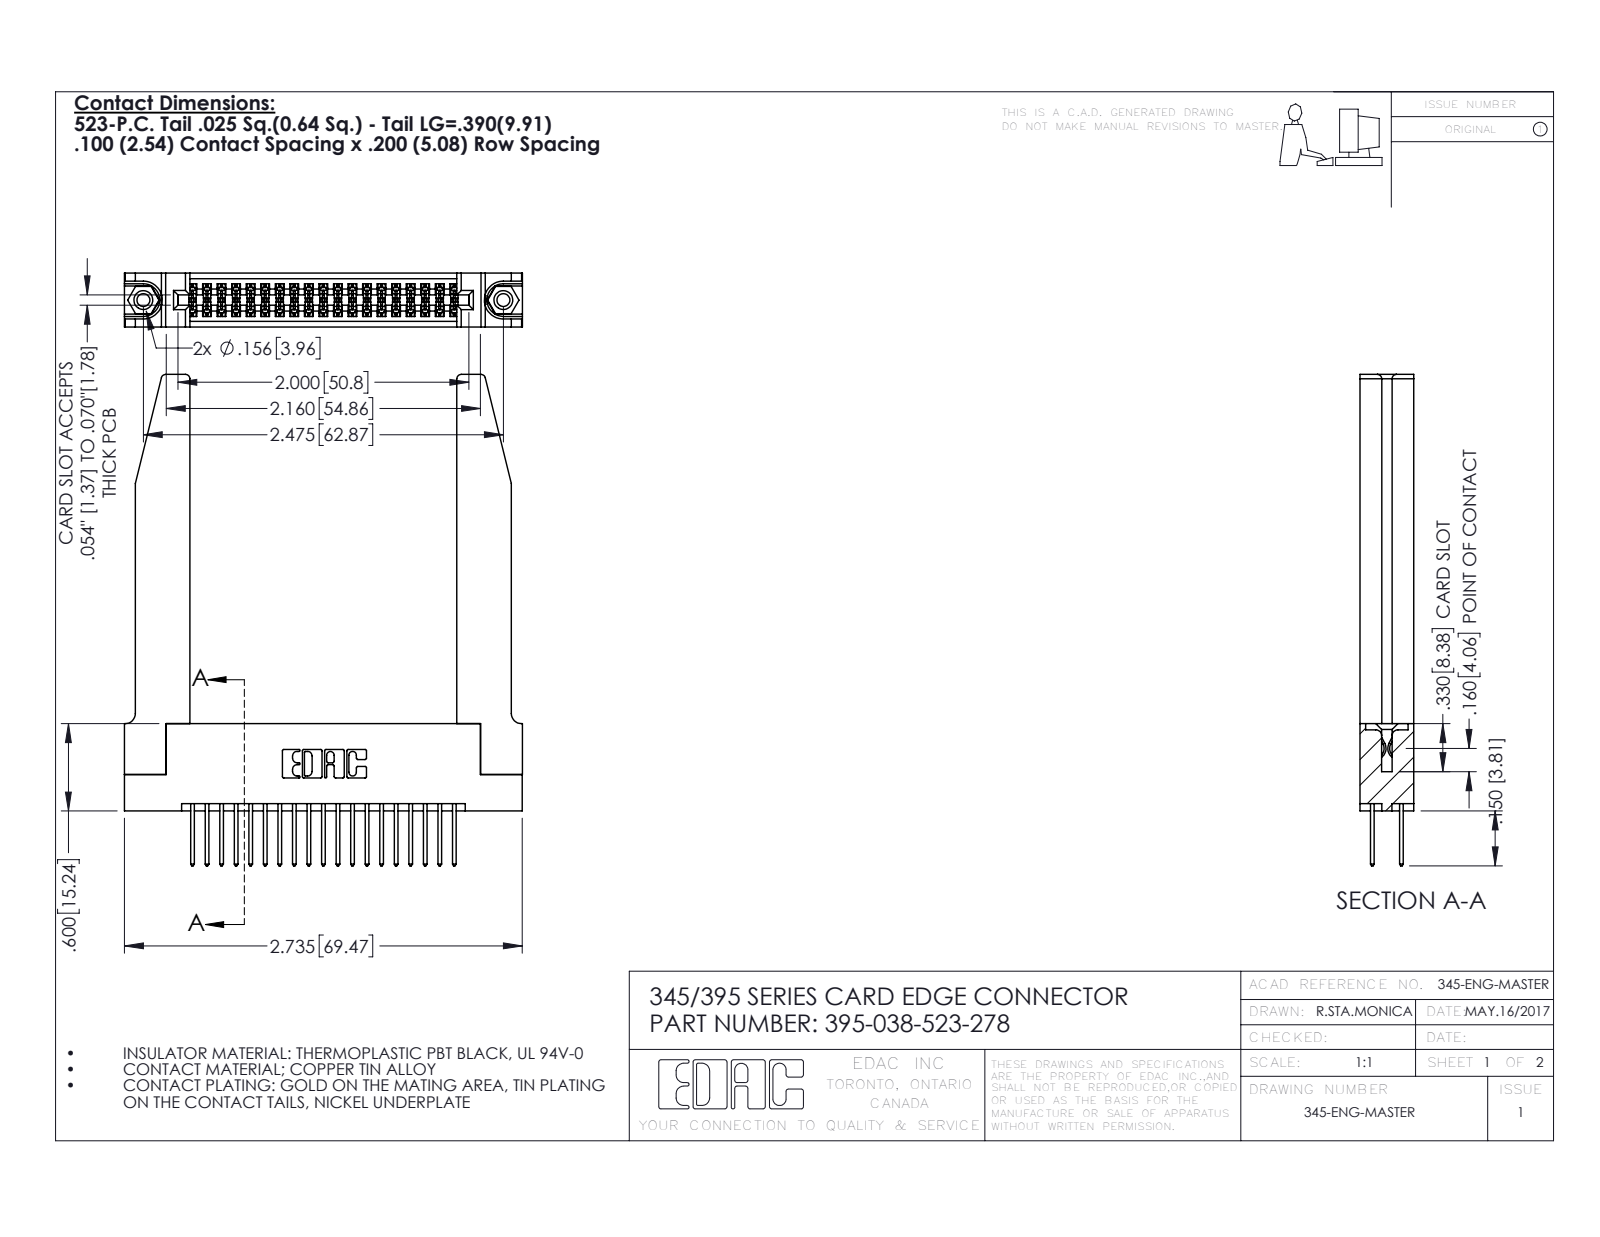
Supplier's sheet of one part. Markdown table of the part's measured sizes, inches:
| quantity | value |
| --- | --- |
| part name | 345-220-078_345-220-078; 395-038-523-278; 345-250-001_345-250-001-102; 345-292-001_345-293-123 (+1 more) |
| STEP written by | SolidWorks 2016 (CONFIG_CONTROL_DESIGN) |
| units | inches |
| bodies | 43 solids, 2260 faces (1476 planar, 732 cylindrical, 52 other) |
| overall size | 3.377 × 2.736 × 0.37 |
| volume | 0.878 in³ |
| surface area | 25.61 in² |
| round holes (diameter × count) | 0.089 × 2, 0.125 × 2, 0.156 × 2, 0.064 × 1 |
| round bosses / shafts (diameter × count) | 0.155 × 2 |
| partial cylindrical surfaces (radius × count) | 0.006 × 57, 0.01 × 38, 0.01 × 22, 0.03 × 8, 0.007 × 6, 0.031 × 6, 0.026 × 3, 0.014 × 2 |
| main face-to-face distances | 0.37, 0.072, 0.298, 0.2, 0.098, 0.272, 0.025, 0.225, 0.148, 0.15 |
| hole center spacings | 0.27, 2.241, 2.475 |
